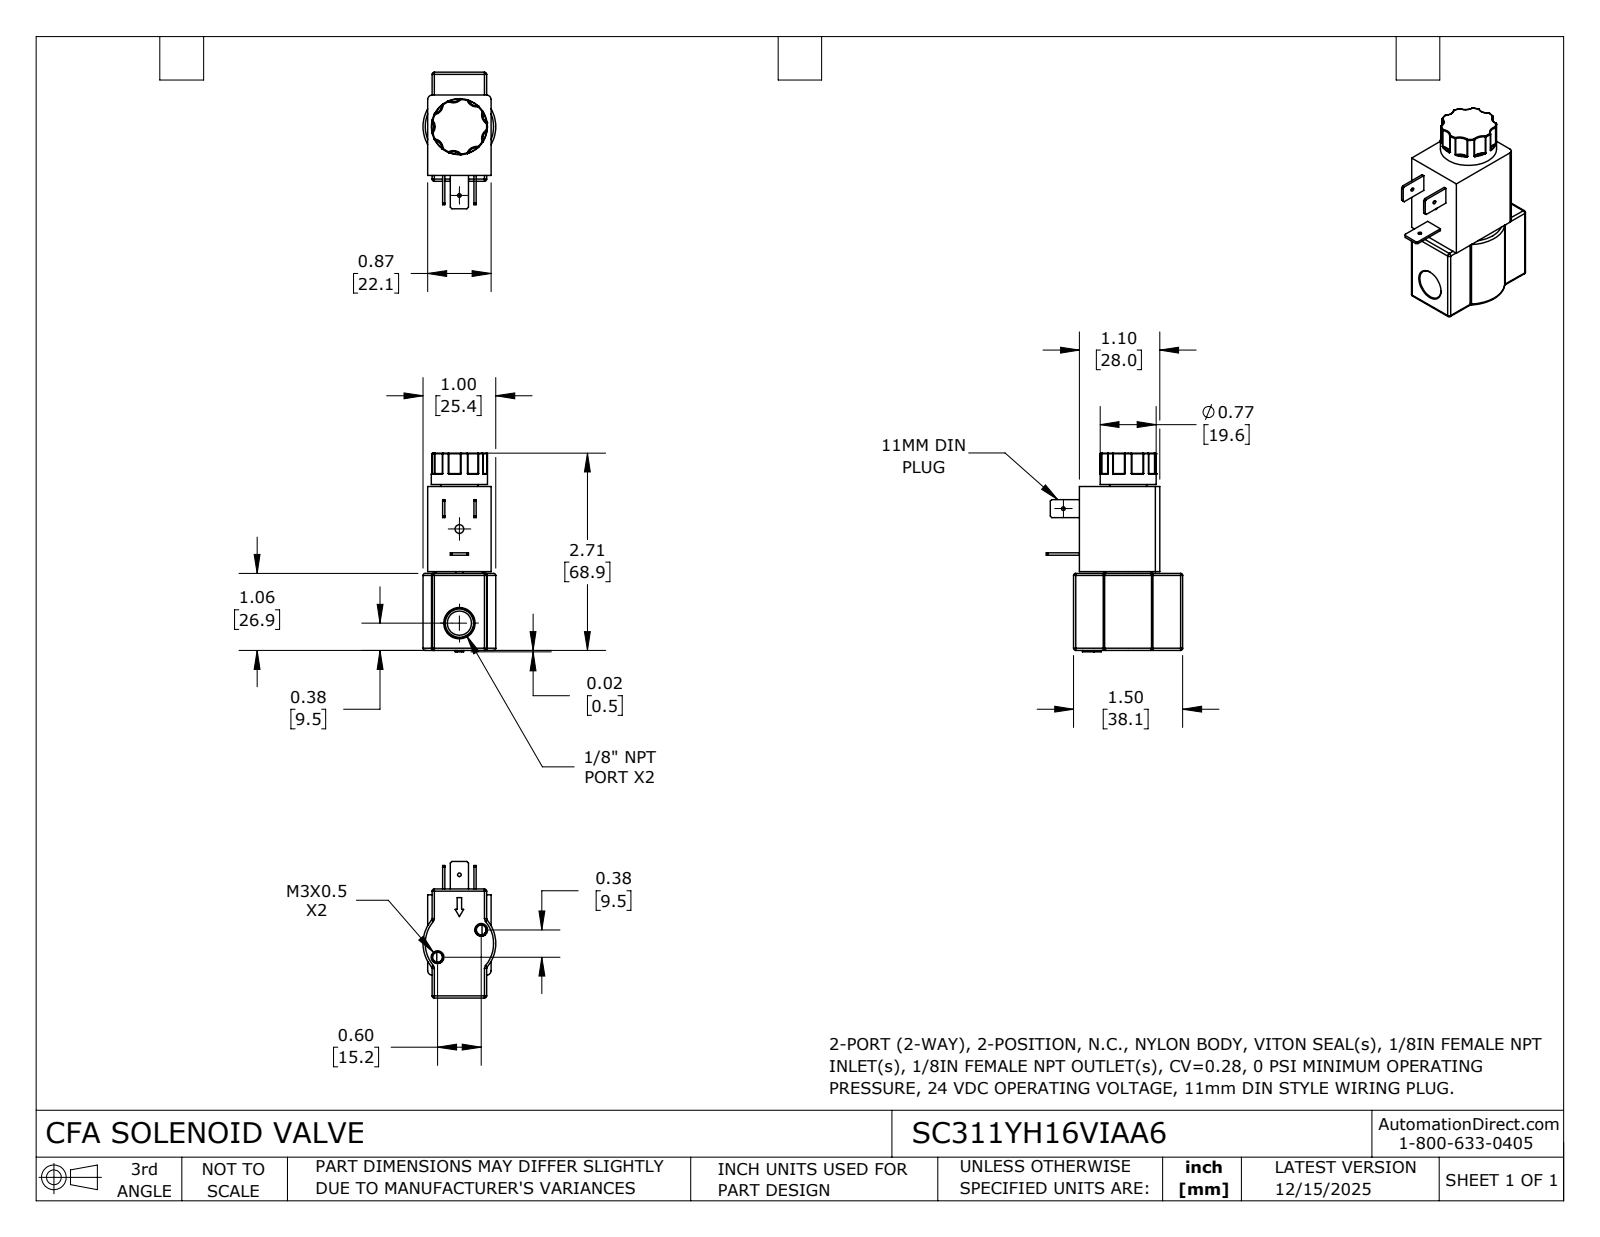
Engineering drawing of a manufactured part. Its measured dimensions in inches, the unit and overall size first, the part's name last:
Units: inches
Overall size (bounding box): 2.732 × 1.877 × 1
Round holes (diameter × count): ⌀0.05 ×2, ⌀0.136 ×2, ⌀0.12 ×1, ⌀0.332 ×1
Round bosses / shafts (diameter × count): ⌀0.77 ×1
Partial cylindrical surfaces — rounded edges, fillets, slot ends (radius × count): R0.01 ×18, R0.03 ×16, R0.133 ×7, R0.06 ×2, R0.132 ×2, R0.295 ×2, R0.311 ×1, R0.5 ×1
Main face-to-face distances: 0.06, 0.81, 0.87, 1.104, 2.252, 1.06, 1.192, 0.75, 1.085, 0.025
Hole centre spacings: 0.707, 0.815, 1.172, 1.293
Volume: 2.516 in³ · Surface area: 17.12 in²
Bodies: 1 solid, 383 faces (62 planar, 117 cylindrical, 204 other)
Part name (STEP PRODUCT): SC311YH16VIAA6
STEP written by: SolidWorks 2024 (CONFIG_CONTROL_DESIGN)
